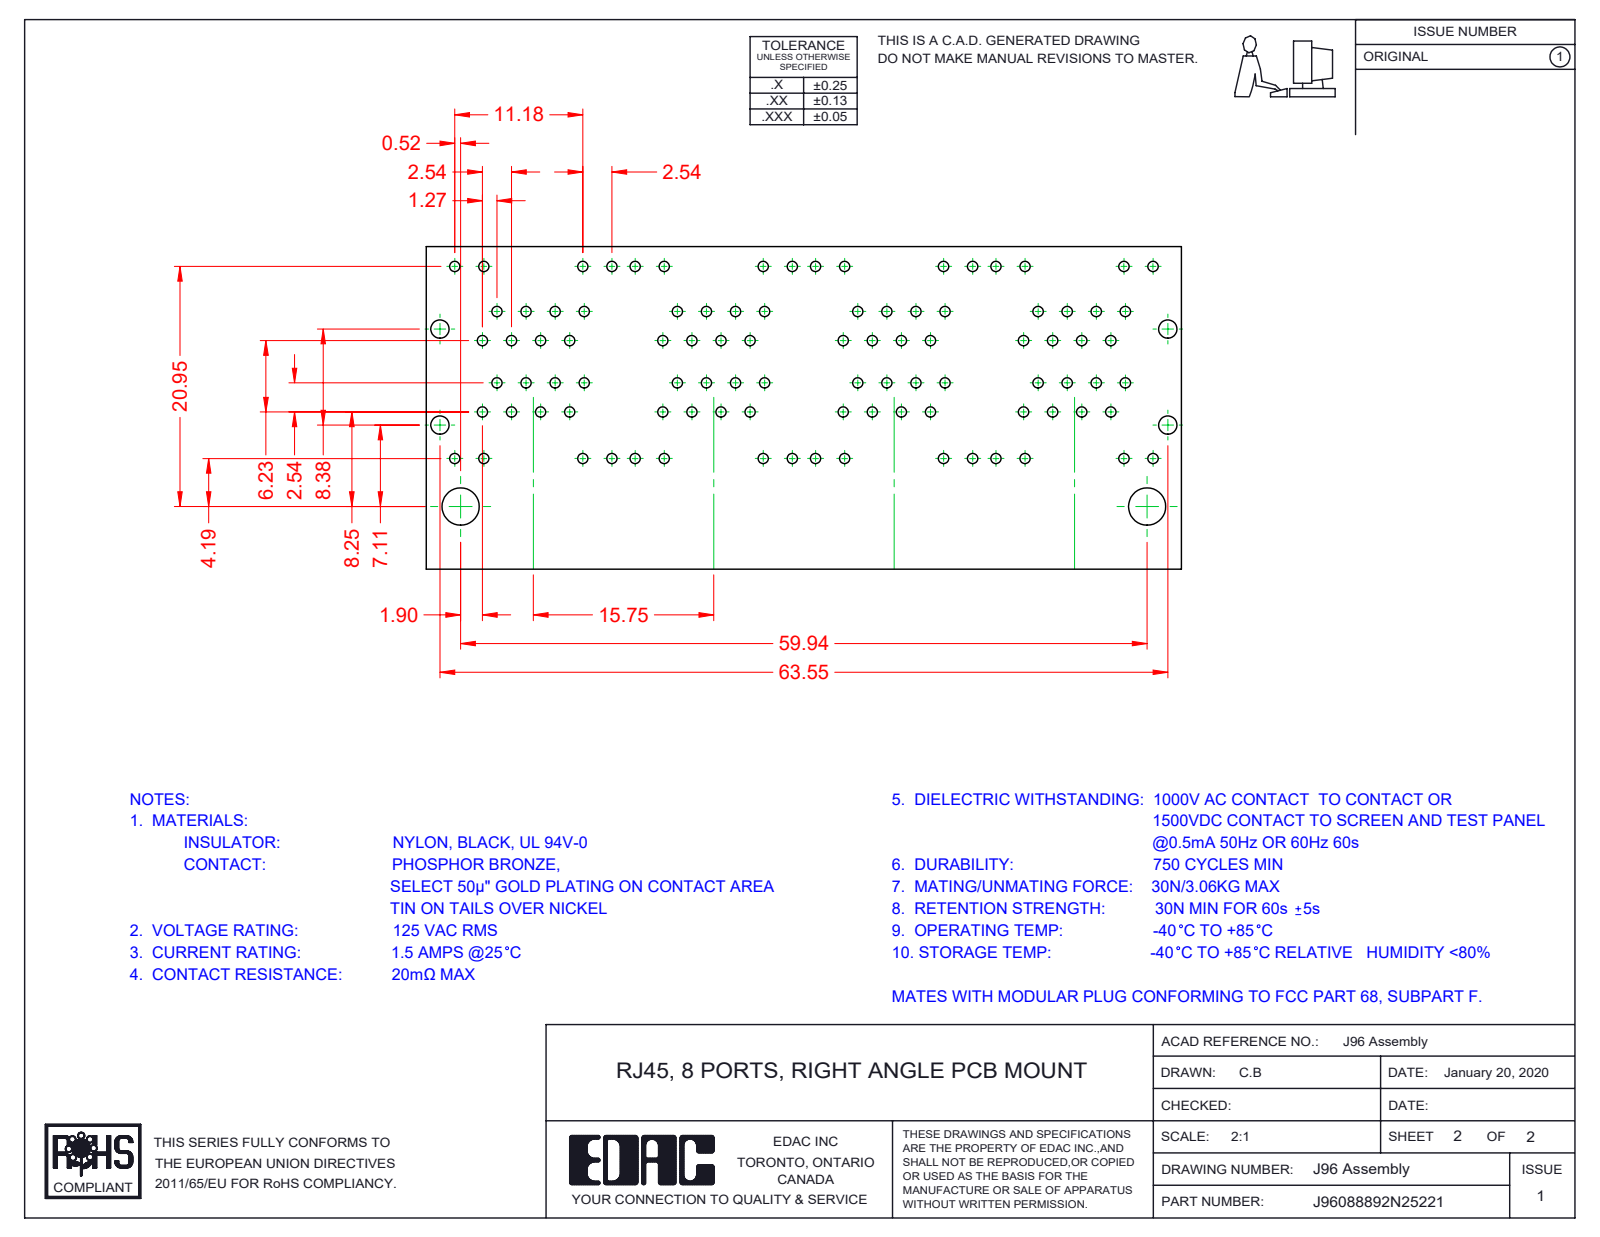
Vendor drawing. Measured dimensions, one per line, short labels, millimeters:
name: 96 Contacts Upper; 96 Grounding_8 Ports; 96 Insulator Insert; 96 Contacts Lower (+8 more)
written by: SolidWorks 2016 (CONFIG_CONTROL_DESIGN)
unit: mm
bodies: 96 solids, 7820 faces (6105 planar, 1404 cylindrical, 311 other)
size: 67.35 × 31.38 × 28.68
volume: 24 149 mm³; area: 63 596 mm²
holes: 3× ⌀1.7
bosses: 3× ⌀1.68
rounds: 124× R0.25, 73× R0.35, 72× R1, 49× R0.5, 32× R0.91, 27× R0.2, 14× R0.27, 11× R0.7
face distances: 15.75, 0.35, 9.95, 1.17, 1.6, 0.54, 9.98, 10.18, 12.67, 3.37
hole spacings: 15.75, 31.5
